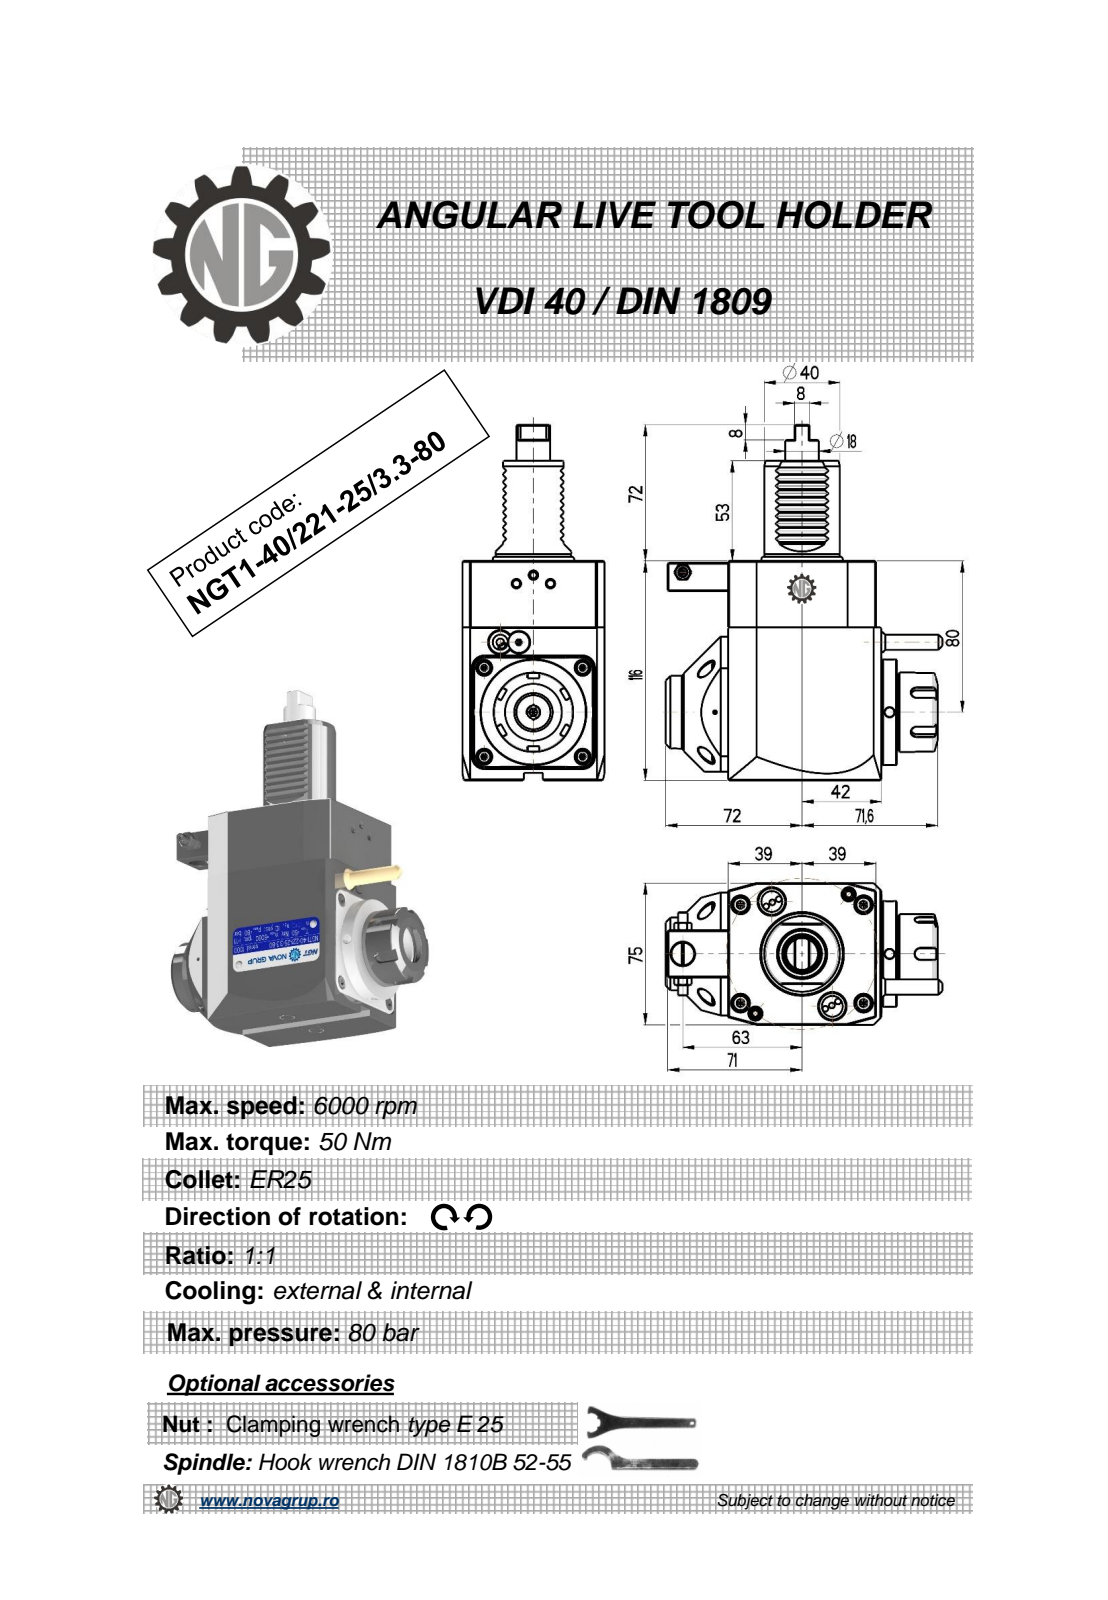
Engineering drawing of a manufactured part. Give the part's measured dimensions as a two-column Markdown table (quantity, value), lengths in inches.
| quantity | value |
| --- | --- |
| part name | NGT1_40_221_25_3_3_80 |
| STEP written by | PRO/ENGINEER BY PARAMETRIC TECHNOLOGY CORPORATION, 2010280 (CONFIG_CONTROL_DESIGN) |
| units | inches |
| bodies | 1 solid, 475 faces (228 planar, 96 cylindrical, 151 other) |
| overall size | 7.402 × 5.754 × 2.953 |
| volume | 53.87 in³ |
| surface area | 111.2 in² |
| round holes (diameter × count) | 0.197 × 3, 0.118 × 1, 0.165 × 1, 0.374 × 1, 0.472 × 1, 0.799 × 1 |
| round bosses / shafts (diameter × count) | 2.205 × 1, 1.693 × 1, 1.654 × 1, 1.575 × 1, 1.516 × 1, 1.299 × 1, 0.701 × 1, 0.441 × 1 |
| partial cylindrical surfaces (radius × count) | 0.012 × 20, 0.01 × 12, 0.009 × 6, 0.118 × 5, 0.031 × 2, 1.575 × 1 |
| main face-to-face distances | 2.953, 4.567, 3.189, 3.071, 0.118, 0.433, 0.315, 4.37, 3.181, 0.11 |
| hole center spacings | 1.558, 1.611, 2.854, 4.301, 5.195 |
